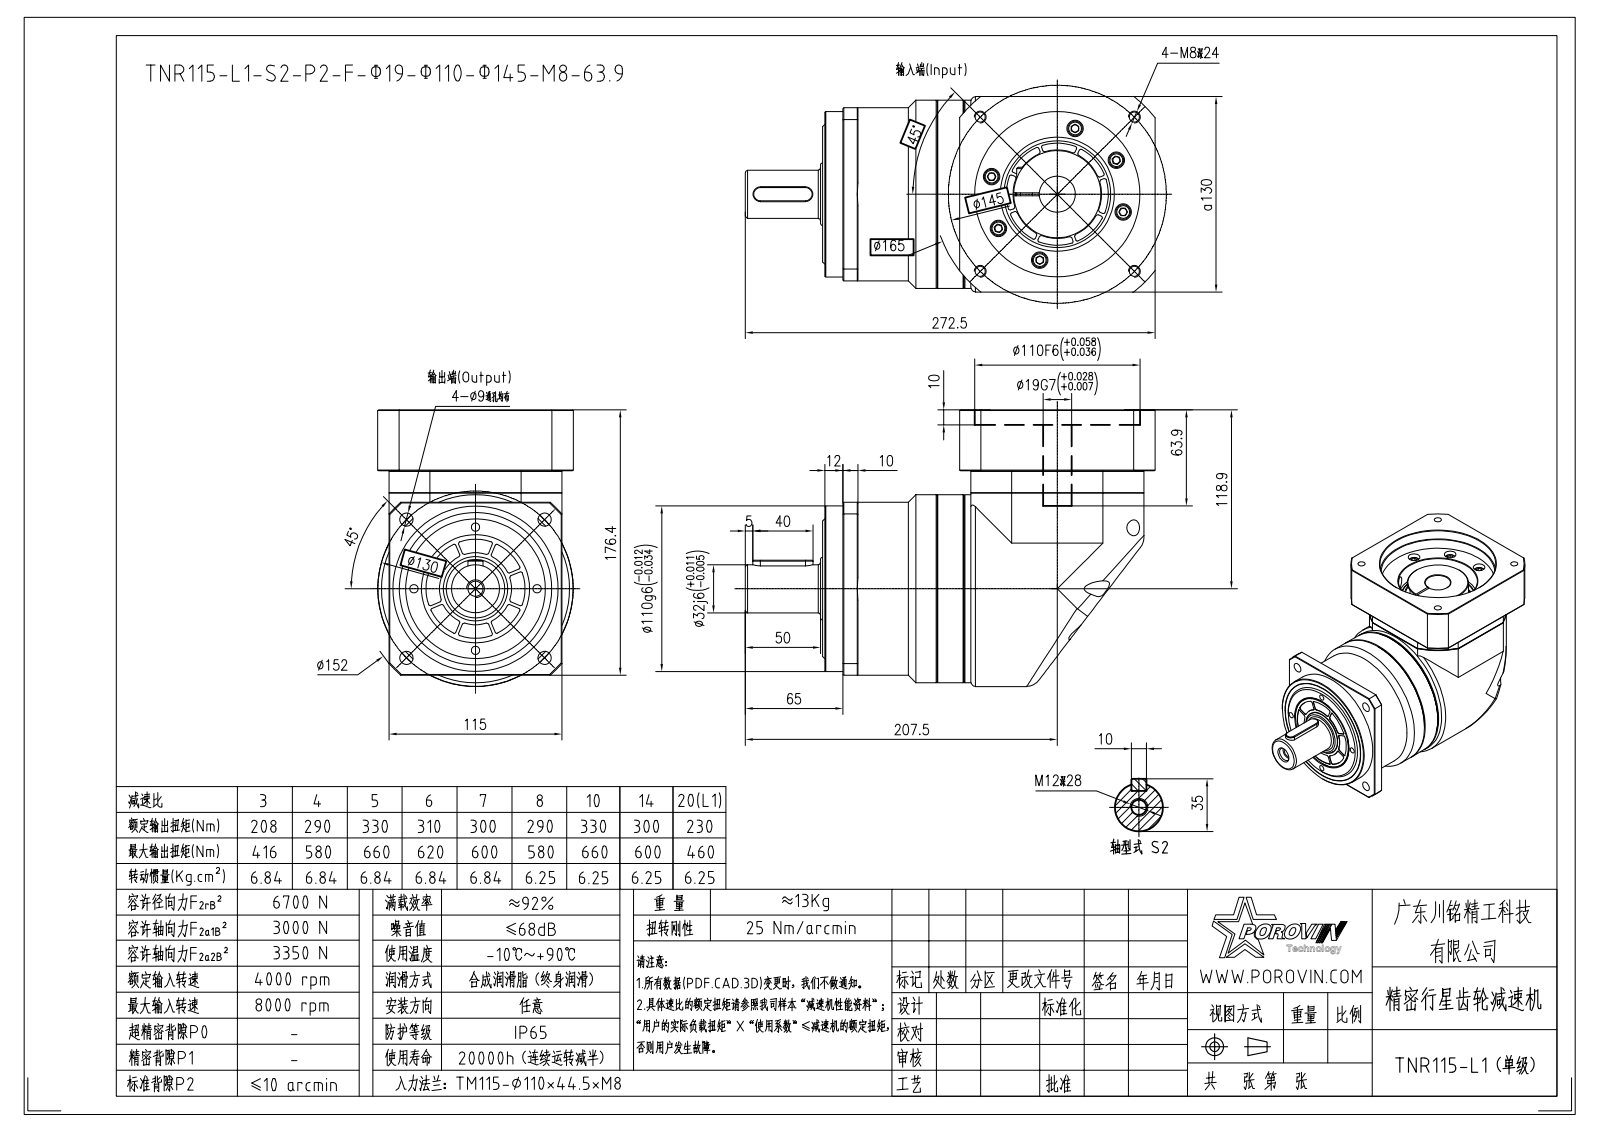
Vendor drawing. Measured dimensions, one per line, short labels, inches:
name: SPRING_LOCK_WASHERS--NORMAL_TYP; TNR115190001; HEXAGON_SOCKET_HEAD_CAP_S-22522; 65X55X700 (+8 more)
written by: CREO PARAMETRIC BY PTC INC, 2020053 (CONFIG_CONTROL_DESIGN)
unit: in
bodies: 50 solids, 1383 faces (575 planar, 556 cylindrical, 252 other)
size: 10.728 × 7.24 × 5.118
volume: 177.9 in³; area: 544.6 in²
holes: 19× ⌀0.263, 13× ⌀0.256, 12× ⌀0.433, 8× ⌀0.197, 7× ⌀0.413, 6× ⌀0.26, 5× ⌀0.268, 4× ⌀0.217, 4× ⌀0.354, 2× ⌀2.835, 1× ⌀0.335, 1× ⌀0.402
bosses: 19× ⌀0.394, 19× ⌀0.389, 19× ⌀0.236, 1× ⌀5.118, 1× ⌀4.921, 1× ⌀4.882, 1× ⌀4.528, 1× ⌀4.331
rounds: 64× R0.039, 3× R0.197, 1× R0.266, 1× R0.394, 1× R2.559, 1× R2.992, 1× R3.248
face distances: 0.709, 0.701, 0.587, 0.295, 4.823, 0.118, 2.181, 0.787, 5.118, 1.594
hole spacings: 1.781, 2.254, 1.818, 2.024, 3.292, 3.89, 4.381, 1.828
